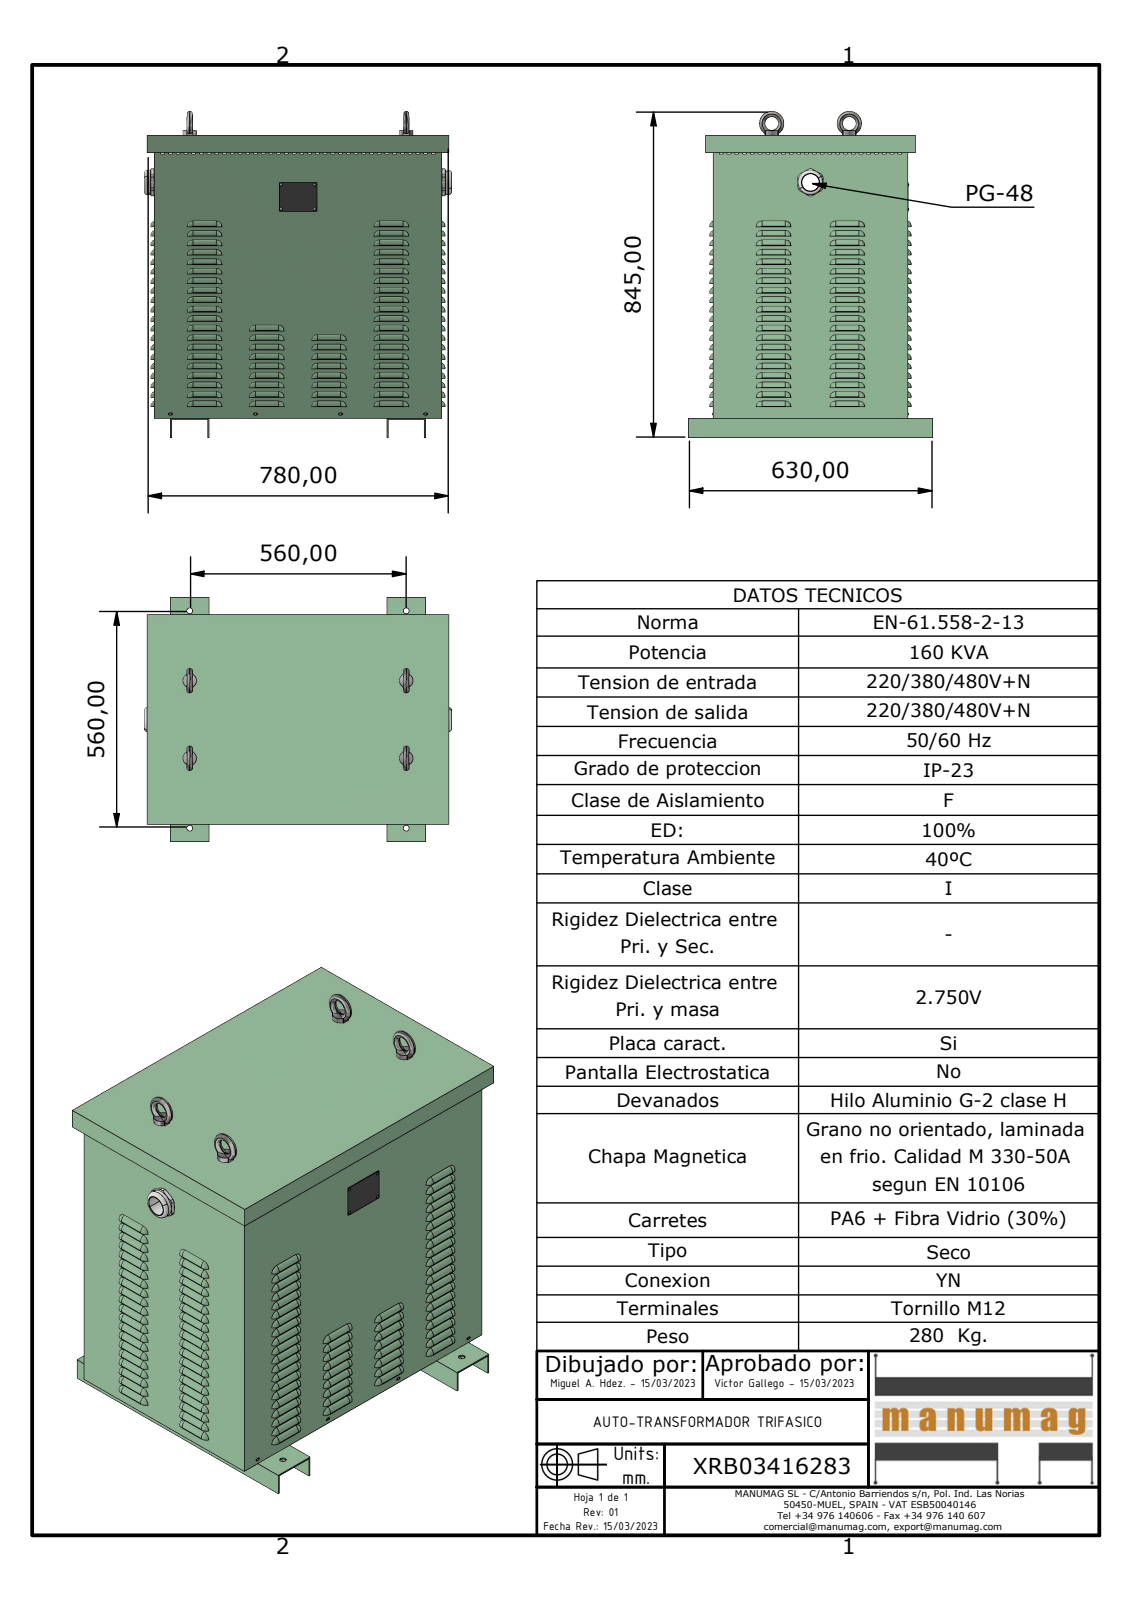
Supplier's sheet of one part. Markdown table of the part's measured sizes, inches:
| quantity | value |
| --- | --- |
| part name | XRB03416283; JE160 EXPORT JE200 EXPORT NACIONAL BASE; JE160 EXPORT JE200 EXPORT NACIONAL PATA; JE160 EXPORT CUERPO (+5 more) |
| STEP written by | Autodesk Inventor 2023 (AUTOMOTIVE_DESIGN) |
| units | inches |
| bodies | 24 solids, 4187 faces (1441 planar, 1866 cylindrical, 880 other) |
| overall size | 33.228 × 31.31 × 24.803 |
| volume | 432.4 in³ |
| surface area | 9 697 in² |
| round holes (diameter × count) | 0.433 × 936, 0.591 × 8, 0.157 × 4, 0.197 × 4, 1.378 × 2, 1.732 × 1, 2.362 × 1 |
| round bosses / shafts (diameter × count) | 0.126 × 8, 0.63 × 4, 0.583 × 4, 2.48 × 3, 2.335 × 1, 2.329 × 1, 2.269 × 1 |
| partial cylindrical surfaces (radius × count) | 0.551 × 194, 0.276 × 84, 0.591 × 80, 0.098 × 8, 0.079 × 4, 0.689 × 4, 1.378 × 1 |
| main face-to-face distances | 0.079, 19.685, 28.74, 29.213, 19.606, 19.764, 28.819, 29.134, 28.661, 29.291 |
| hole center spacings | 0.591, 1.181, 1.32, 8.053, 6.288, 8.031, 5.113, 6.26 |
